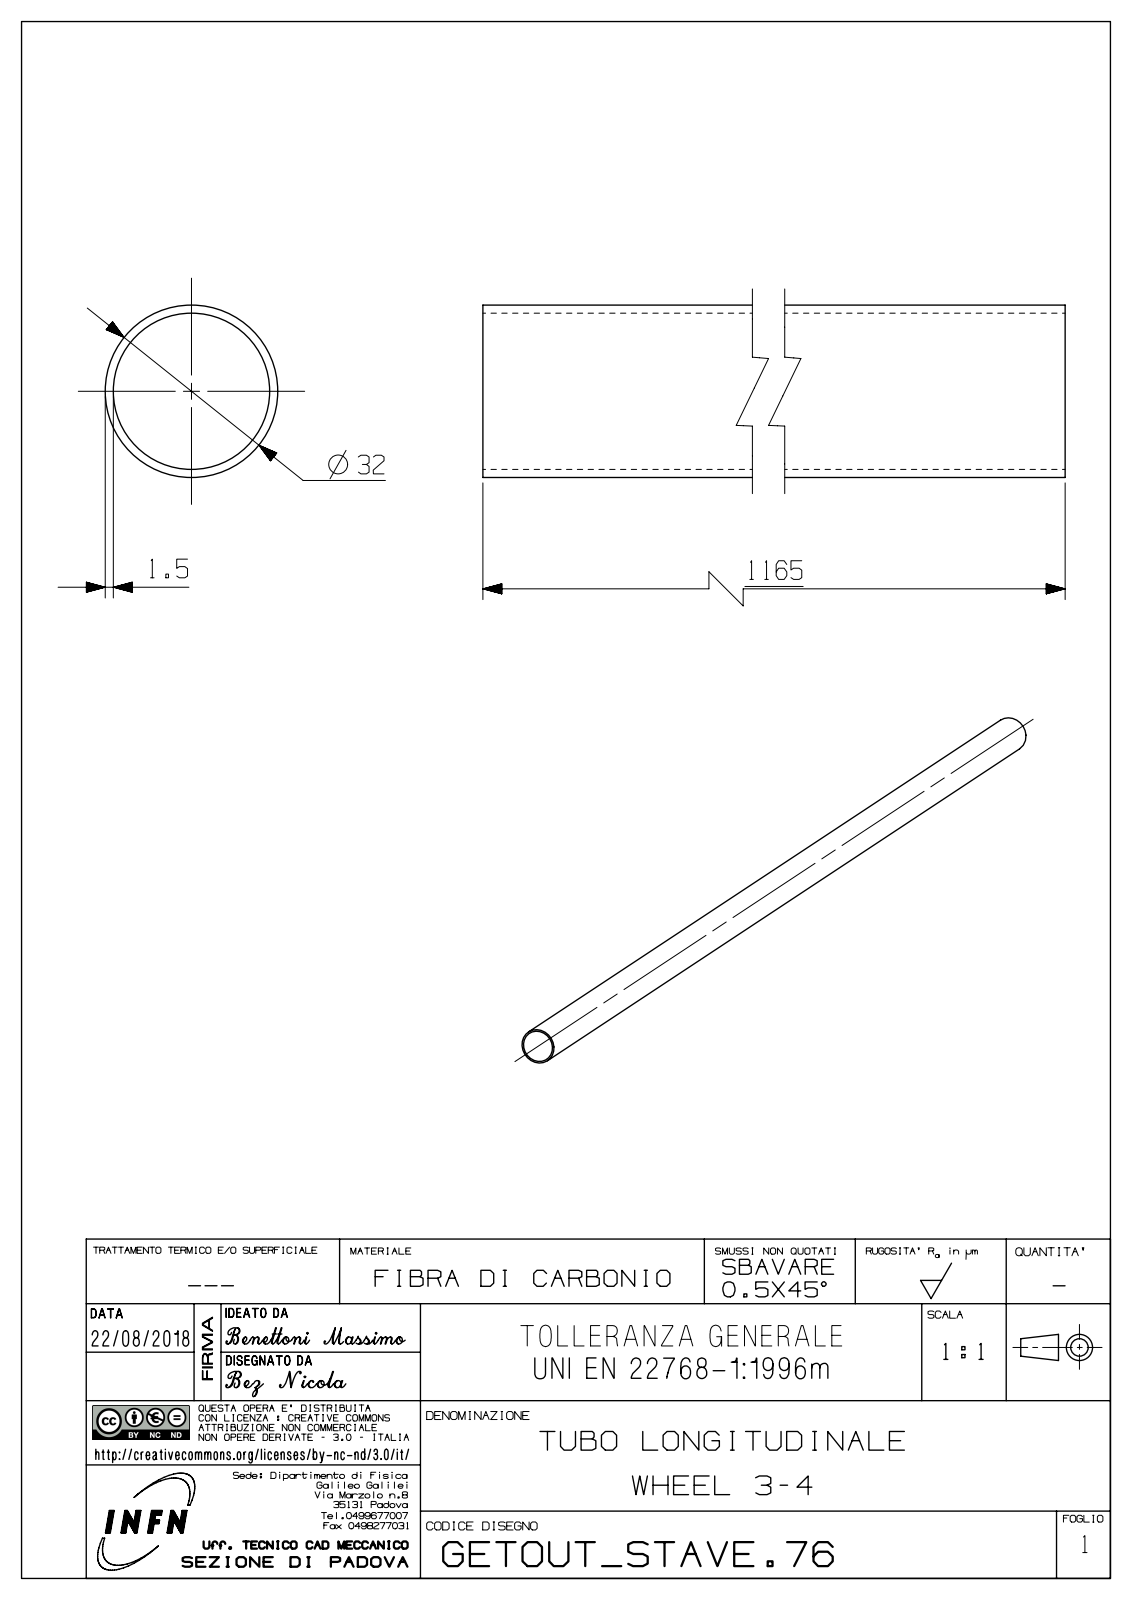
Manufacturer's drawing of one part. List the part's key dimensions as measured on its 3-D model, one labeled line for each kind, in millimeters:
Part name (STEP PRODUCT): bez8324385A6uwa
STEP written by: SIEMENS PLM Software NX 12.0 (AUTOMOTIVE_DESIGN)
Units: millimetres
Bodies: 1 solid, 4 faces (2 planar, 2 cylindrical, 0 other)
Overall size (bounding box): 1165 × 32 × 32
Volume: 167 443 mm³ · Surface area: 223 545 mm²
Round holes (diameter × count): ⌀29 ×1
Round bosses / shafts (diameter × count): ⌀32 ×1
Main face-to-face distances: 1165
